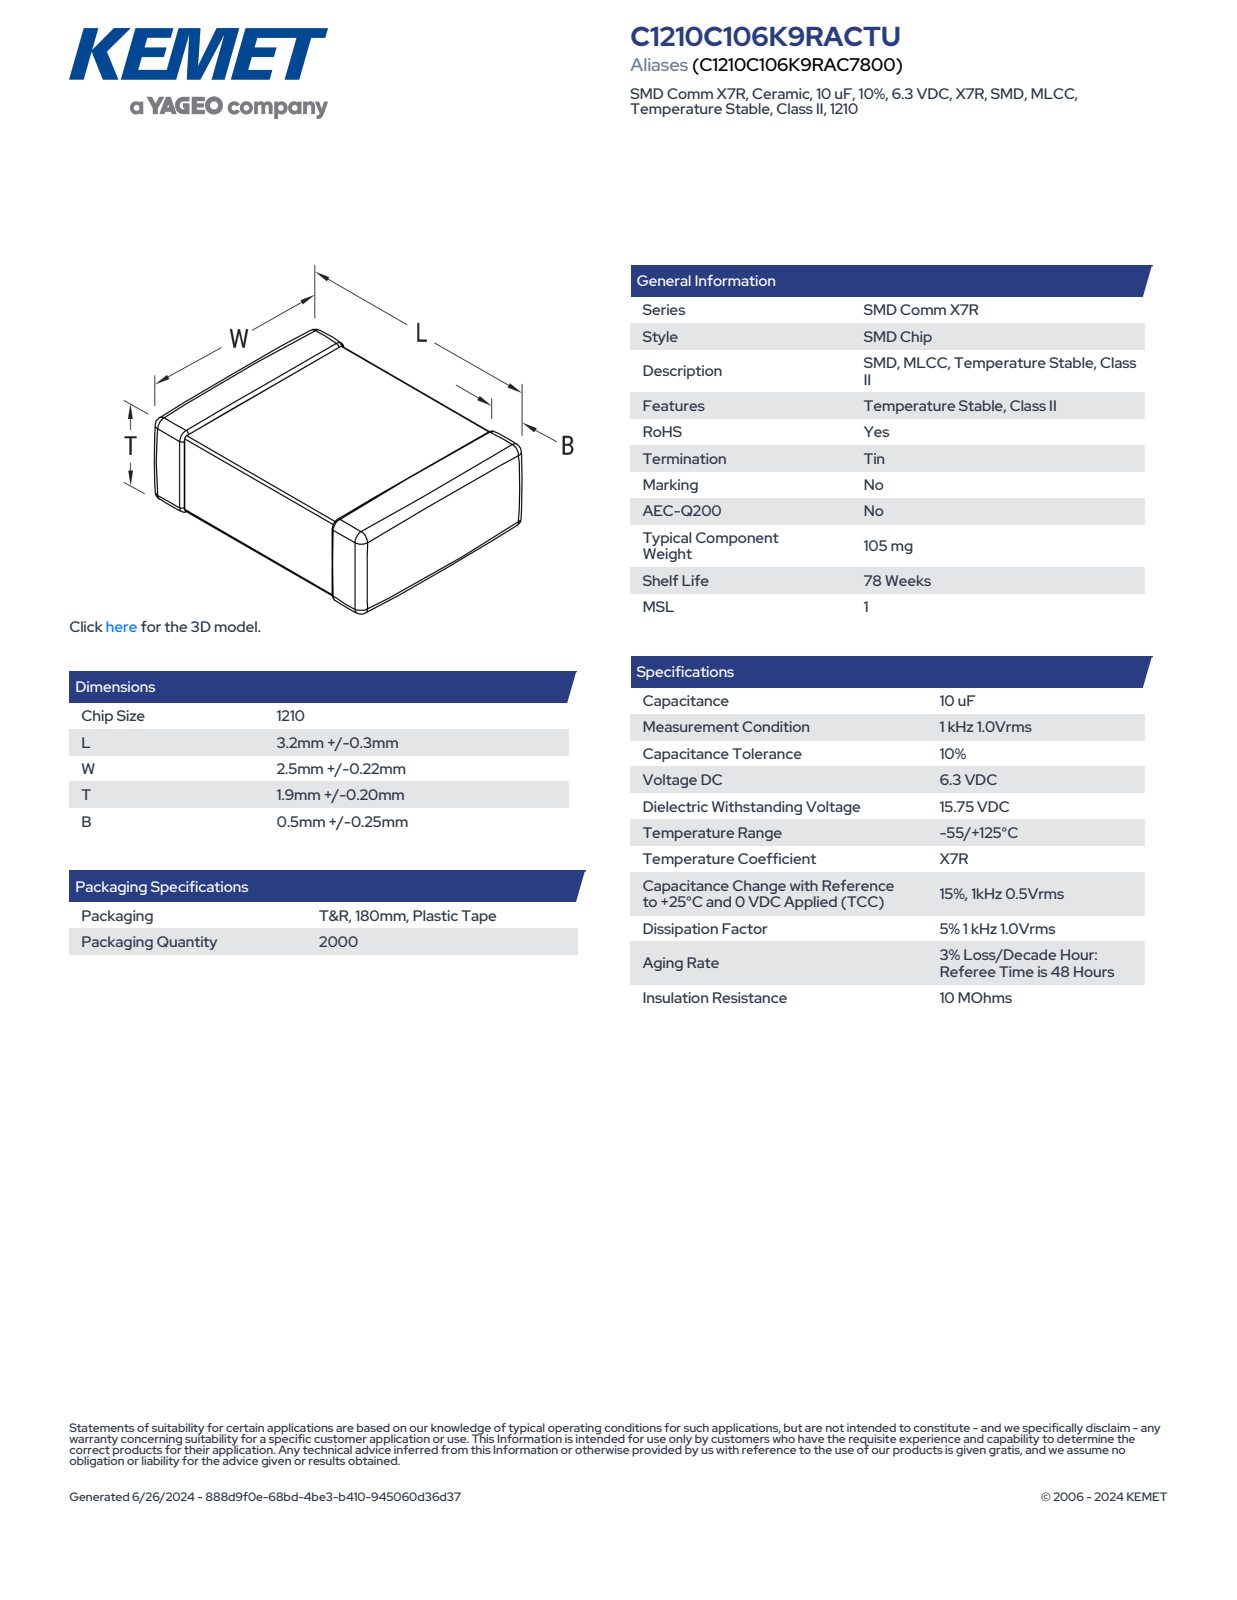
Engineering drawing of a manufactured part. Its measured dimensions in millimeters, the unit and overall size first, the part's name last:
Units: millimetres
Overall size (bounding box): 3.5 × 2.72 × 2.1
Main face-to-face distances: 2.04, 3.5, 2.66, 1.98, 2.6, 2.1, 2.72, 2.05, 1.99, 1.31
Volume: 19 mm³ · Surface area: 44 mm²
Bodies: 4 solids, 125 faces (71 planar, 38 cylindrical, 16 other)
Part name (STEP PRODUCT): CCS_CCSTDNOS_1210_L3.5W2.72T2.1B0.75
STEP written by: SolidWorks 2014 (AUTOMOTIVE_DESIGN)
